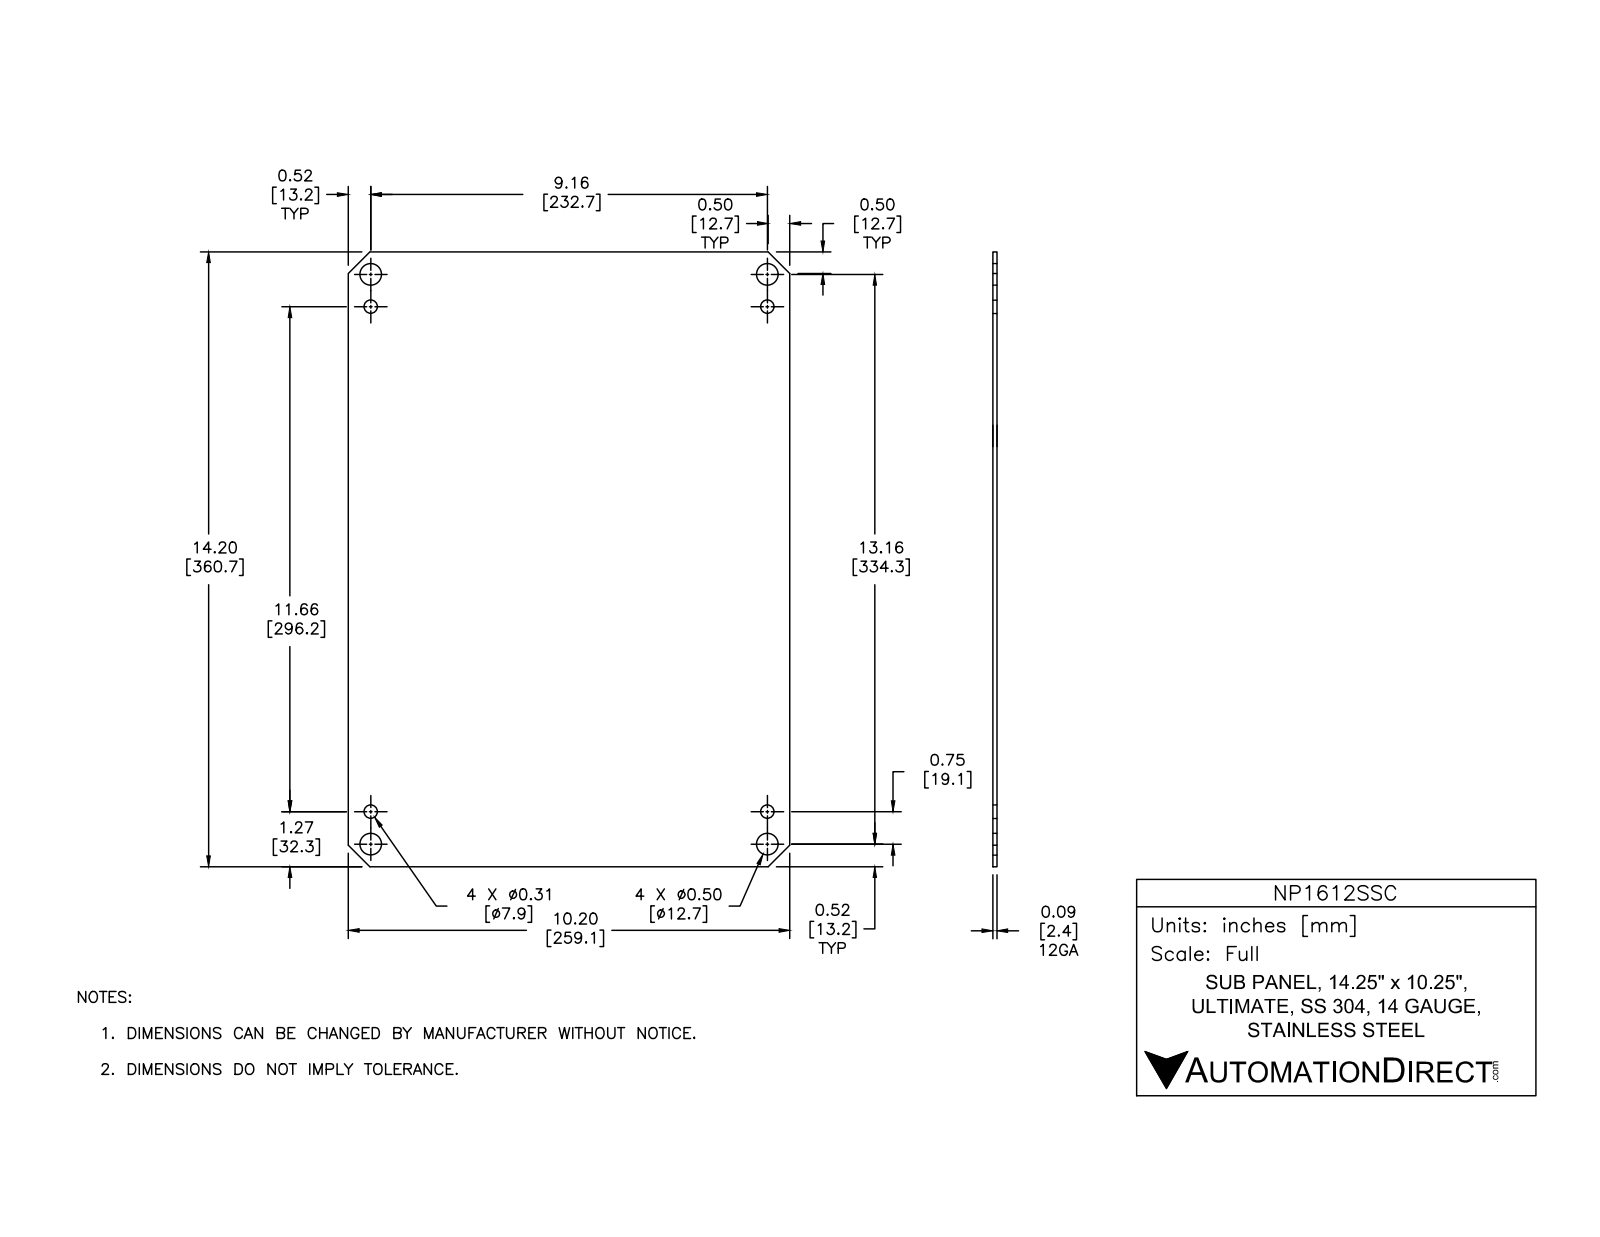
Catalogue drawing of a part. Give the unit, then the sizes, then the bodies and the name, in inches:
Units: inches
Overall size (bounding box): 14.2 × 10.2 × 0.094
Round holes (diameter × count): ⌀0.313 ×4, ⌀0.5 ×4
Main face-to-face distances: 0.094, 10.2, 14.2, 16.544
Hole centre spacings: 0.75, 9.16, 9.191, 12.41, 15.424, 11.66, 13.16, 14.828
Volume: 13.43 in³ · Surface area: 291.9 in²
Bodies: 1 solid, 18 faces (10 planar, 8 cylindrical, 0 other)
Part name (STEP PRODUCT): NP1612SSC
STEP written by: Autodesk Inventor 2012 (AUTOMOTIVE_DESIGN)
